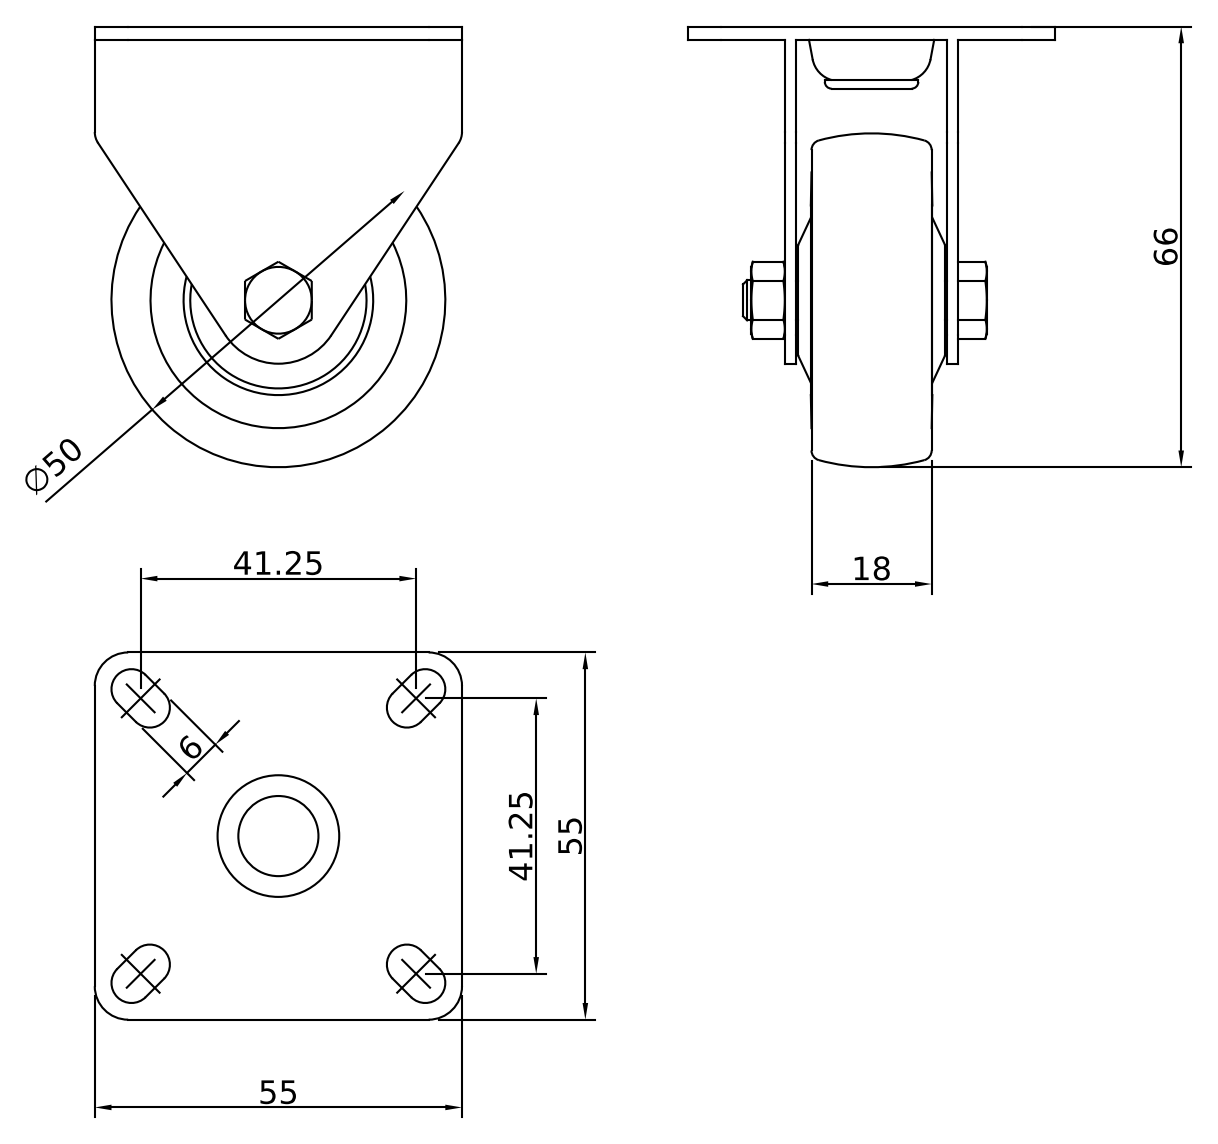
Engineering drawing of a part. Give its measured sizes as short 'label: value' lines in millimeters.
name: CRUST0000036; 440000020104; 440000020105; 440000020106 (+3 more)
written by: Autodesk Inventor 2022 (AUTOMOTIVE_DESIGN)
unit: mm
bodies: 7 solids, 155 faces (60 planar, 37 cylindrical, 58 other)
size: 66 × 55 × 55
volume: 44 989 mm³; area: 27 645 mm²
holes: 1× ⌀4.92, 1× ⌀6, 1× ⌀6.2, 1× ⌀6.3, 1× ⌀8, 1× ⌀8.2, 1× ⌀25.4, 1× ⌀28.4
bosses: 1× ⌀26.4, 1× ⌀14, 1× ⌀12, 1× ⌀7.9, 1× ⌀5.9
rounds: 10× R3, 4× R5, 1× R9.5
face distances: 1.75, 24.25, 2, 22.5, 26, 22, 2.25, 4, 20.25, 21.75
